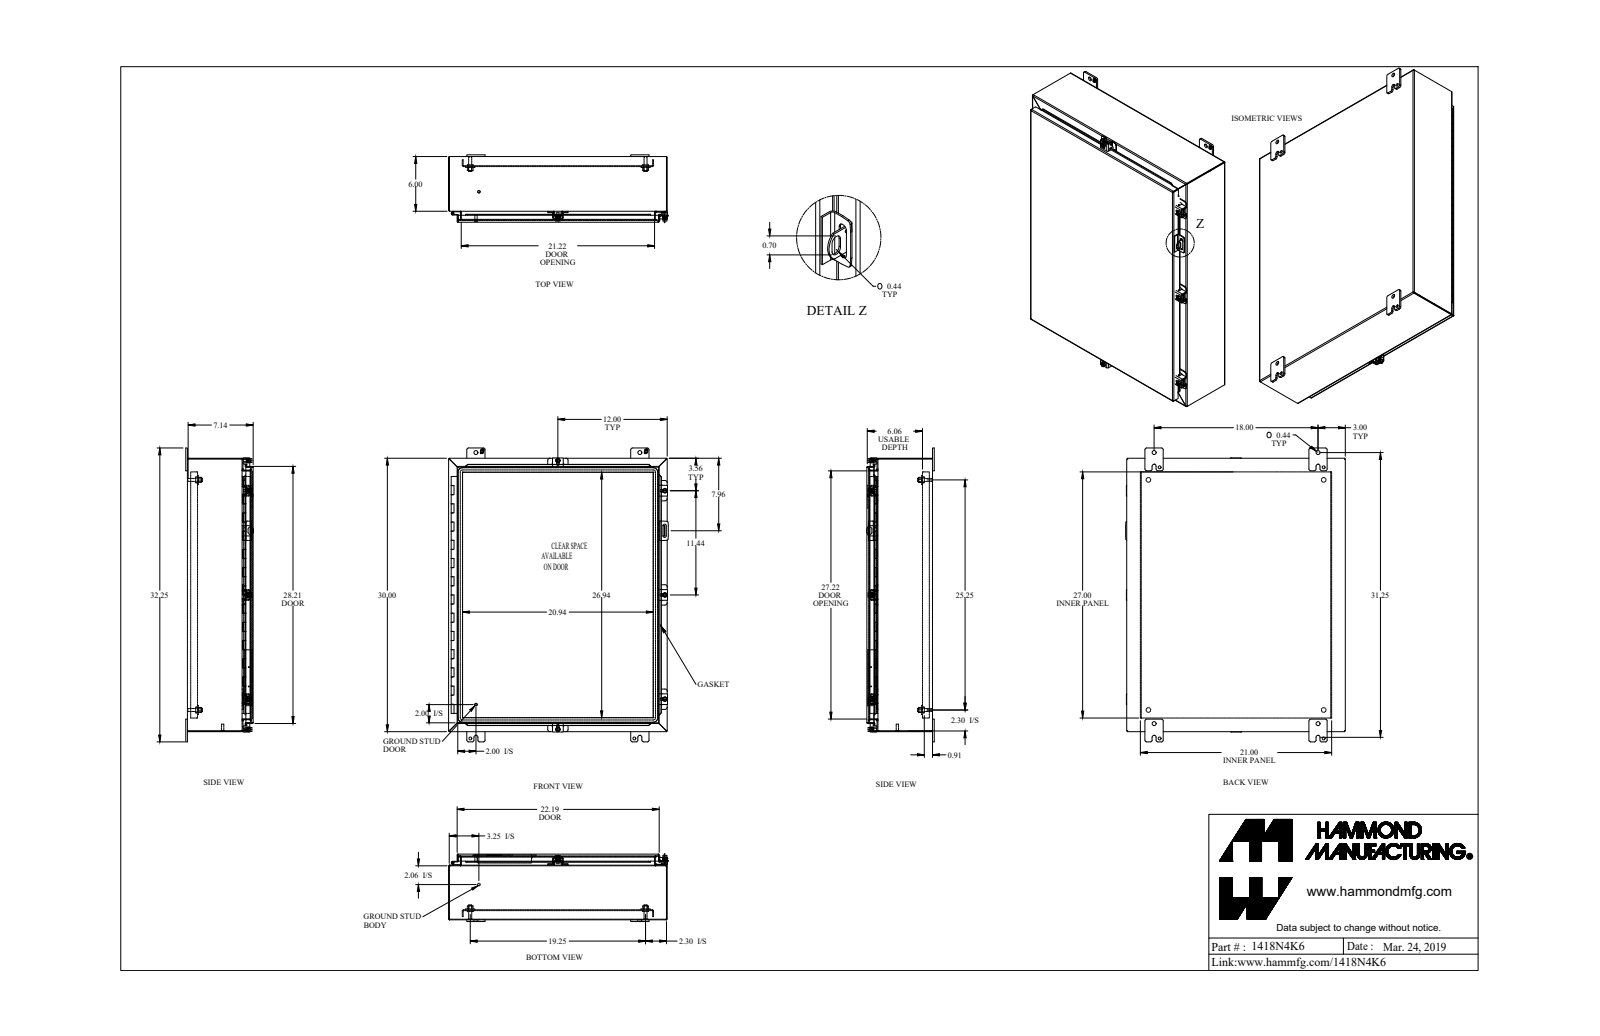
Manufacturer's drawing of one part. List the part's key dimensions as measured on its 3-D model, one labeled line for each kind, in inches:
Part name (STEP PRODUCT): 1418N4K6_Default
STEP written by: SolidWorks 2019 (CONFIG_CONTROL_DESIGN)
Units: inches
Bodies: 43 solids, 1600 faces (965 planar, 549 cylindrical, 86 other)
Overall size (bounding box): 32.25 × 24.126 × 7.437
Volume: 243.9 in³ · Surface area: 6 346 in²
Round holes (diameter × count): ⌀0.213 ×5, ⌀0.265 ×5, ⌀0.375 ×5, ⌀0.313 ×4, ⌀0.437 ×4, ⌀0.5 ×4, ⌀0.307 ×2, ⌀0.445 ×2, ⌀0.125 ×1, ⌀0.187 ×1
Round bosses / shafts (diameter × count): ⌀0.5 ×5, ⌀0.39 ×5, ⌀0.244 ×5, ⌀0.65 ×4, ⌀0.375 ×4, ⌀0.33 ×4, ⌀1 ×2, ⌀0.281 ×2
Partial cylindrical surfaces — rounded edges, fillets, slot ends (radius × count): R0.048 ×27, R0.143 ×27, R0.188 ×26, R0.036 ×24, R0.108 ×24, R0.25 ×24, R0.125 ×10, R0.141 ×10
Main face-to-face distances: 0.072, 0.072, 7.066, 7.138, 7.138, 7.21, 0.095, 6.106, 6.034, 1.032
Hole centre spacings: 3.065, 18, 29.018, 1.736, 2.434, 9.857, 9.857, 19.25
